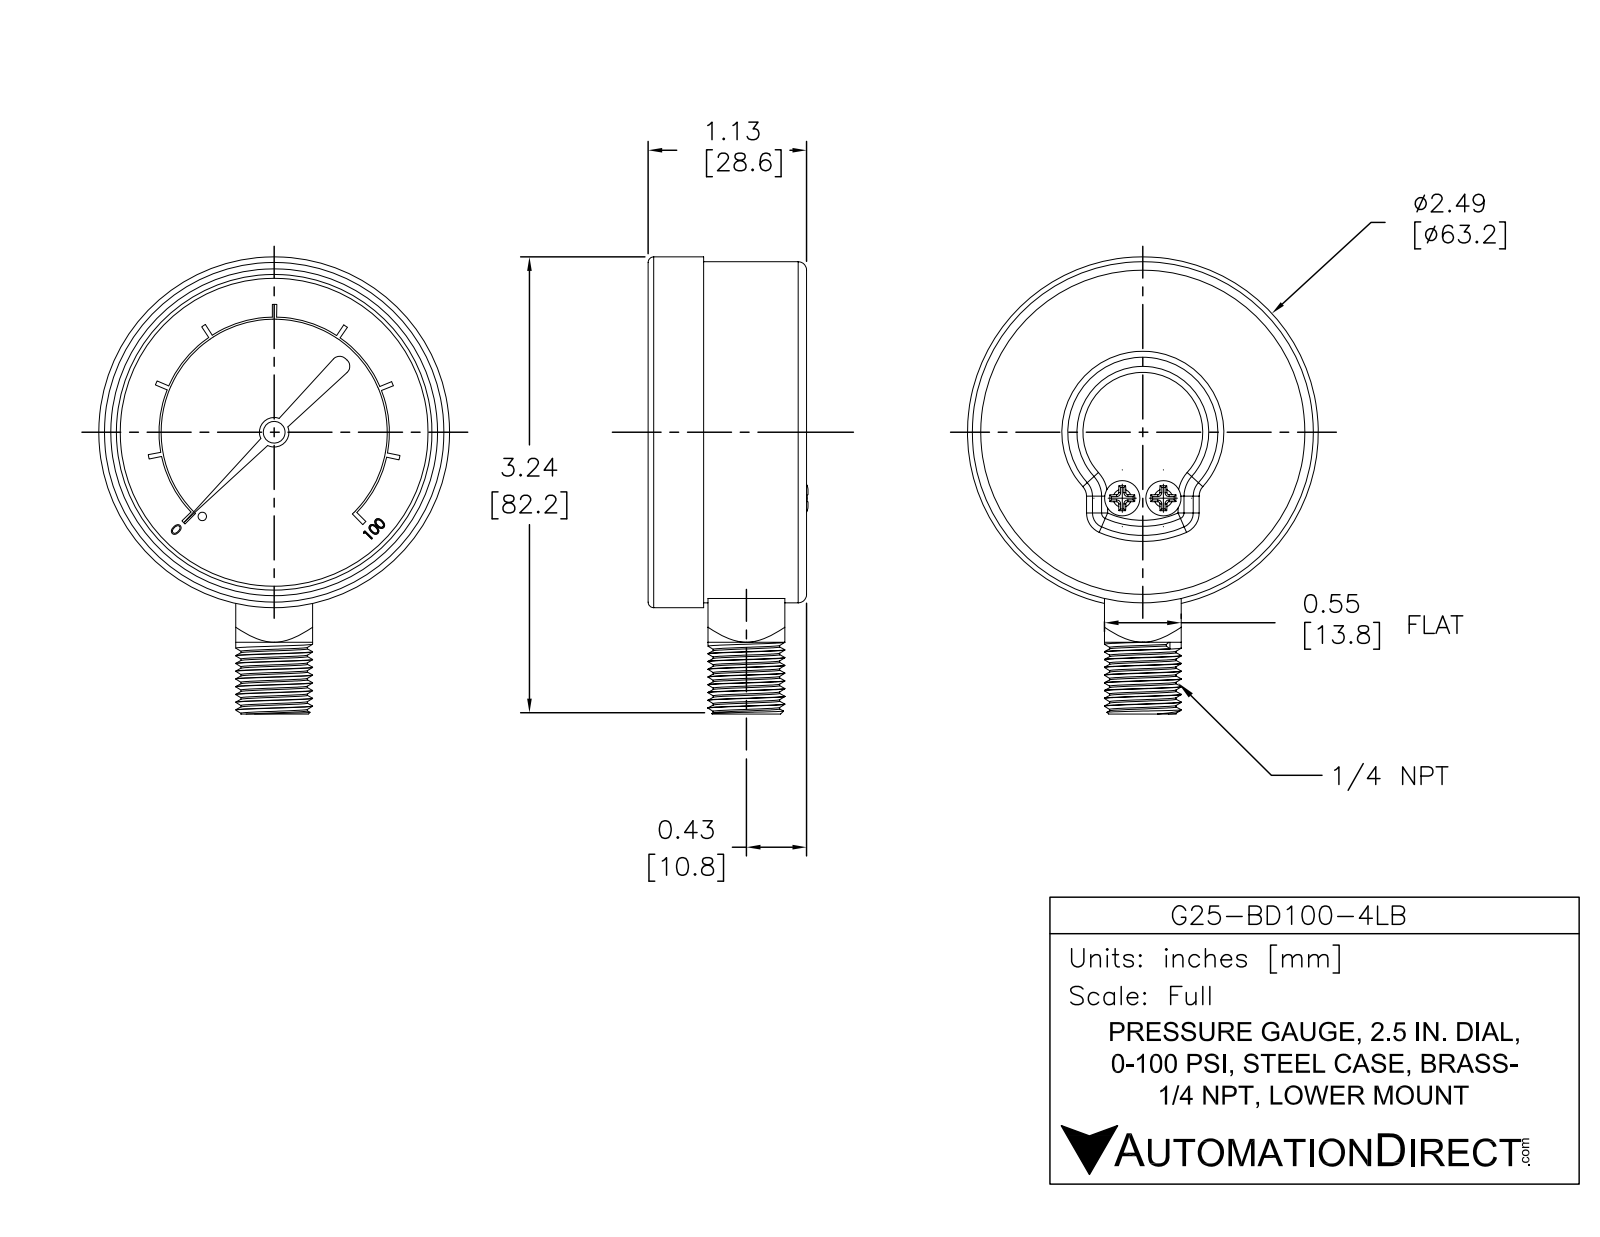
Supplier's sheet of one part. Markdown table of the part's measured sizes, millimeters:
| quantity | value |
| --- | --- |
| part name | G25-BD100-4LB |
| STEP written by | SolidWorks 2021 (AUTOMOTIVE_DESIGN) |
| units | millimeters |
| bodies | 1 solid, 214 faces (115 planar, 35 cylindrical, 64 other) |
| overall size | 82.4 × 63.2 × 28.8 |
| volume | 70 270 mm³ |
| surface area | 14 450 mm² |
| round holes (diameter × count) | 3.6 × 1, 55.5 × 1 |
| round bosses / shafts (diameter × count) | 6.4 × 2, 63.2 × 1, 61.5 × 1, 13.8 × 1, 3.9 × 1, 3.1 × 1, 1.5 × 1 |
| partial cylindrical surfaces (radius × count) | 1.5 × 6, 2.7 × 1, 20.4 × 1, 20.8 × 1 |
| main face-to-face distances | 21.2, 2.5, 18.7, 28.6, 26, 7.4, 13.8, 18.6, 16, 2.6 |
